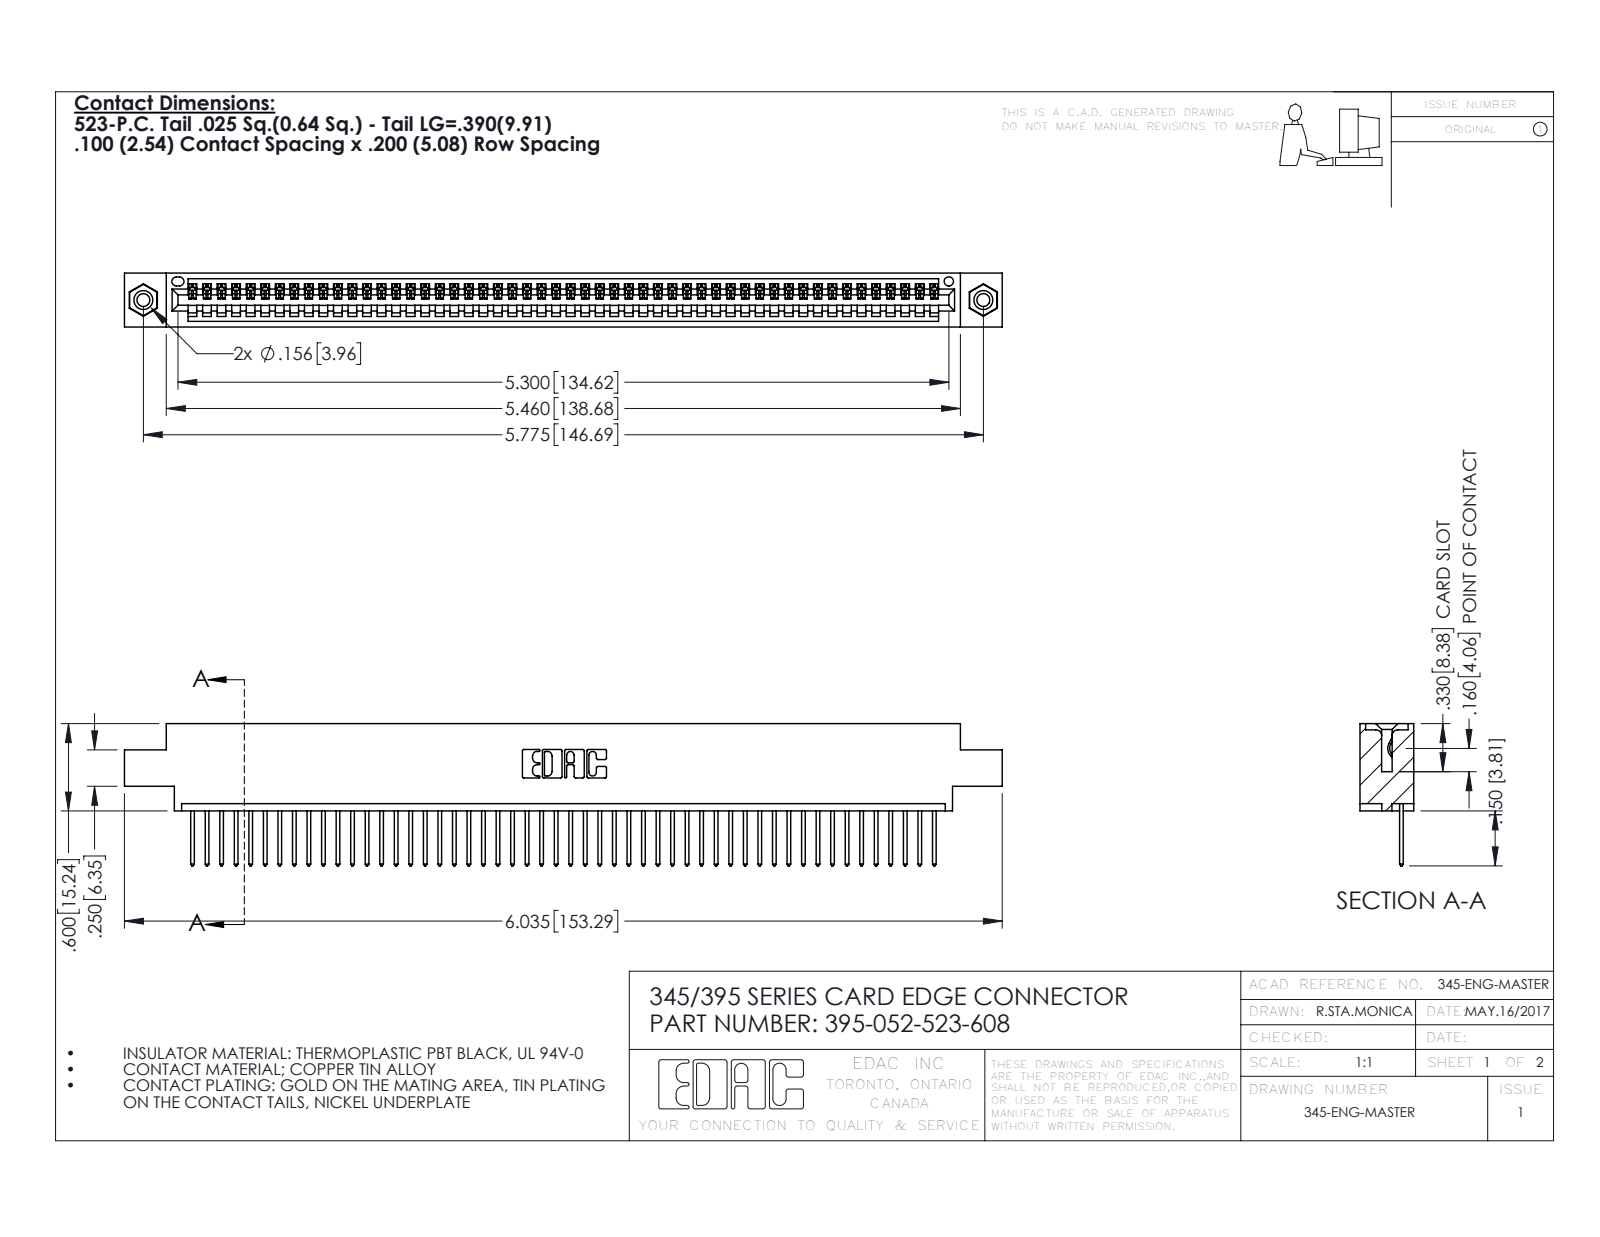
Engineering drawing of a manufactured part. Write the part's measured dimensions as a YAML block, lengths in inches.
part_name: "395-052-523-608; 345-250-001_345-250-003-102; 345-292-001_345-293-123; 345 Part_0.170 Offset - 0.156 Dia-TI"
step_written_by: "SolidWorks 2016 (CONFIG_CONTROL_DESIGN)"
units: inches
bodies: {solids: 55, faces: 3206, planar: 2196, cylindrical: 994, other: 16}
overall_size: [6.035, 0.977, 0.37]
volume: 0.885
surface_area: 30.39
round_holes:
  - {diameter: 0.089, count: 2}
  - {diameter: 0.125, count: 2}
  - {diameter: 0.156, count: 2}
  - {diameter: 0.064, count: 1}
round_bosses_or_shafts:
  - {diameter: 0.155, count: 2}
partial_cylinders:
  - {radius: 0.006, count: 104}
  - {radius: 0.01, count: 104}
  - {radius: 0.01, count: 22}
  - {radius: 0.007, count: 6}
  - {radius: 0.031, count: 6}
  - {radius: 0.026, count: 3}
  - {radius: 0.031, count: 2}
  - {radius: 0.04, count: 2}
face_to_face_distances: [0.072, 0.298, 0.37, 0.098, 0.272, 0.025, 0.2, 0.225, 0.175, 0.149]
hole_center_spacings: [0.27, 5.539, 5.775]
